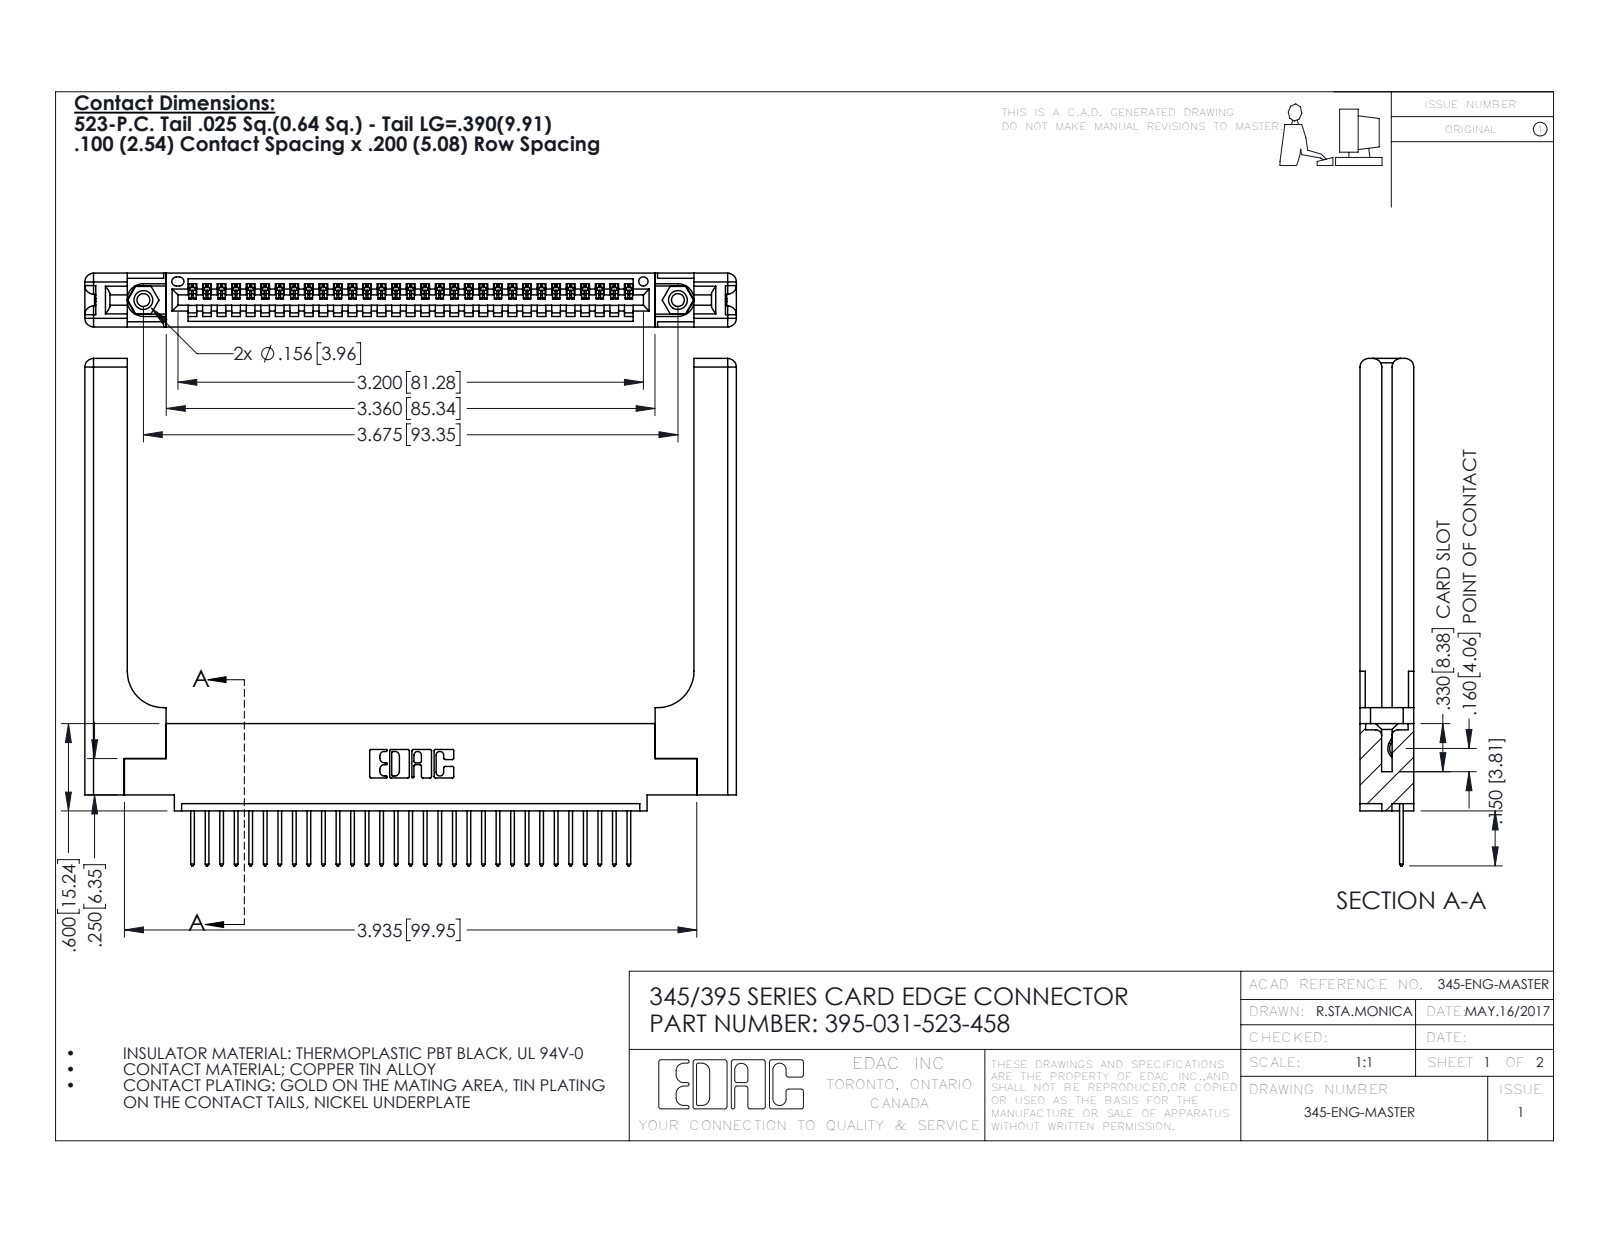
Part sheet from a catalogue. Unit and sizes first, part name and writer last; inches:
Units: inches
Overall size (bounding box): 4.479 × 3.487 × 0.37
Round holes (diameter × count): ⌀0.089 ×2, ⌀0.125 ×2, ⌀0.156 ×2, ⌀0.064 ×1
Round bosses / shafts (diameter × count): ⌀0.155 ×2
Partial cylindrical surfaces — rounded edges, fillets, slot ends (radius × count): R0.006 ×62, R0.01 ×62, R0.01 ×22, R0.06 ×16, R0.007 ×6, R0.031 ×6, R0.026 ×3, R0.03 ×2
Main face-to-face distances: 0.37, 0.072, 0.298, 0.098, 0.272, 0.025, 0.2, 0.148, 0.15, 0.077
Hole centre spacings: 0.27, 3.44, 3.675
Volume: 1.168 in³ · Surface area: 30.07 in²
Bodies: 36 solids, 2184 faces (1472 planar, 652 cylindrical, 60 other)
Part name (STEP PRODUCT): 345 Part_0.110 Offset - 0.156 Dia-TH; 345-250-001_345-250-001-102; 395-031-523-458; 345-292-001_345-293-123 (+1 more)
STEP written by: SolidWorks 2016 (CONFIG_CONTROL_DESIGN)
